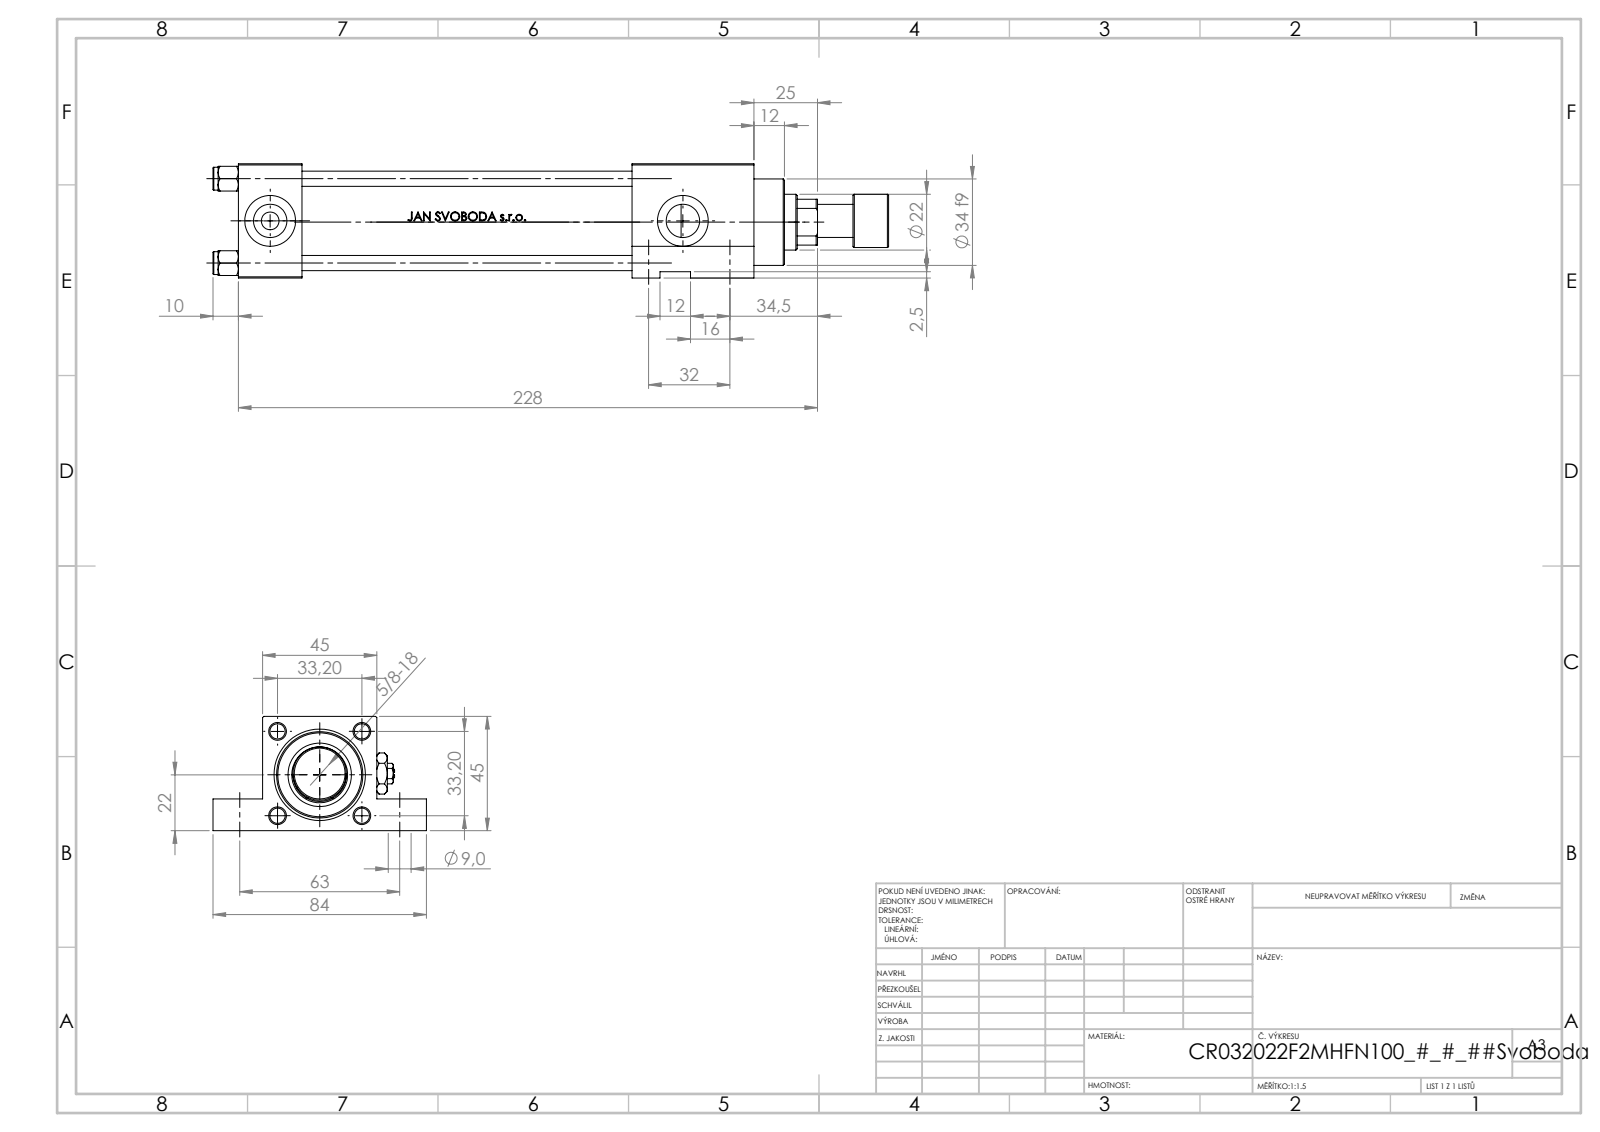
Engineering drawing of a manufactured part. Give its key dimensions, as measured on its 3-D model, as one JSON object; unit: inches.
{"part_name": "V215CR_F_Body; V215_VC_A; V215CR_F_TYCINKA; V215CR_VCP_F (+3 more)", "step_written_by": "SolidWorks 2019 (CONFIG_CONTROL_DESIGN)", "units": "inches", "bodies": {"solids": 13, "faces": 1161, "planar": 461, "cylindrical": 134, "other": 566}, "overall_size": [10.472, 3.307, 1.772], "volume_in3": 18.28, "surface_area_in2": 169.3, "round_holes": [[0.236, 4], [0.354, 4], [0.276, 2], [0.518, 2], [0.787, 2], [0.413, 1], [0.512, 1], [0.866, 1], [0.945, 1], [0.984, 1], [1.26, 1], [1.299, 1]], "round_bosses_or_shafts": [[0.354, 4], [1.496, 1], [1.339, 1], [0.827, 1], [0.512, 1]], "partial_cylinders_radius": [[0.413, 1]], "face_to_face_distances": [1.772, 0.984, 7.008, 7.992, 6.102, 5.118, 0.492, 1.28, 1.89, 0.394], "hole_center_spacings": [1.307, 0.911, 0.938, 1.26, 1.848, 2.48, 2.782, 6.398]}
